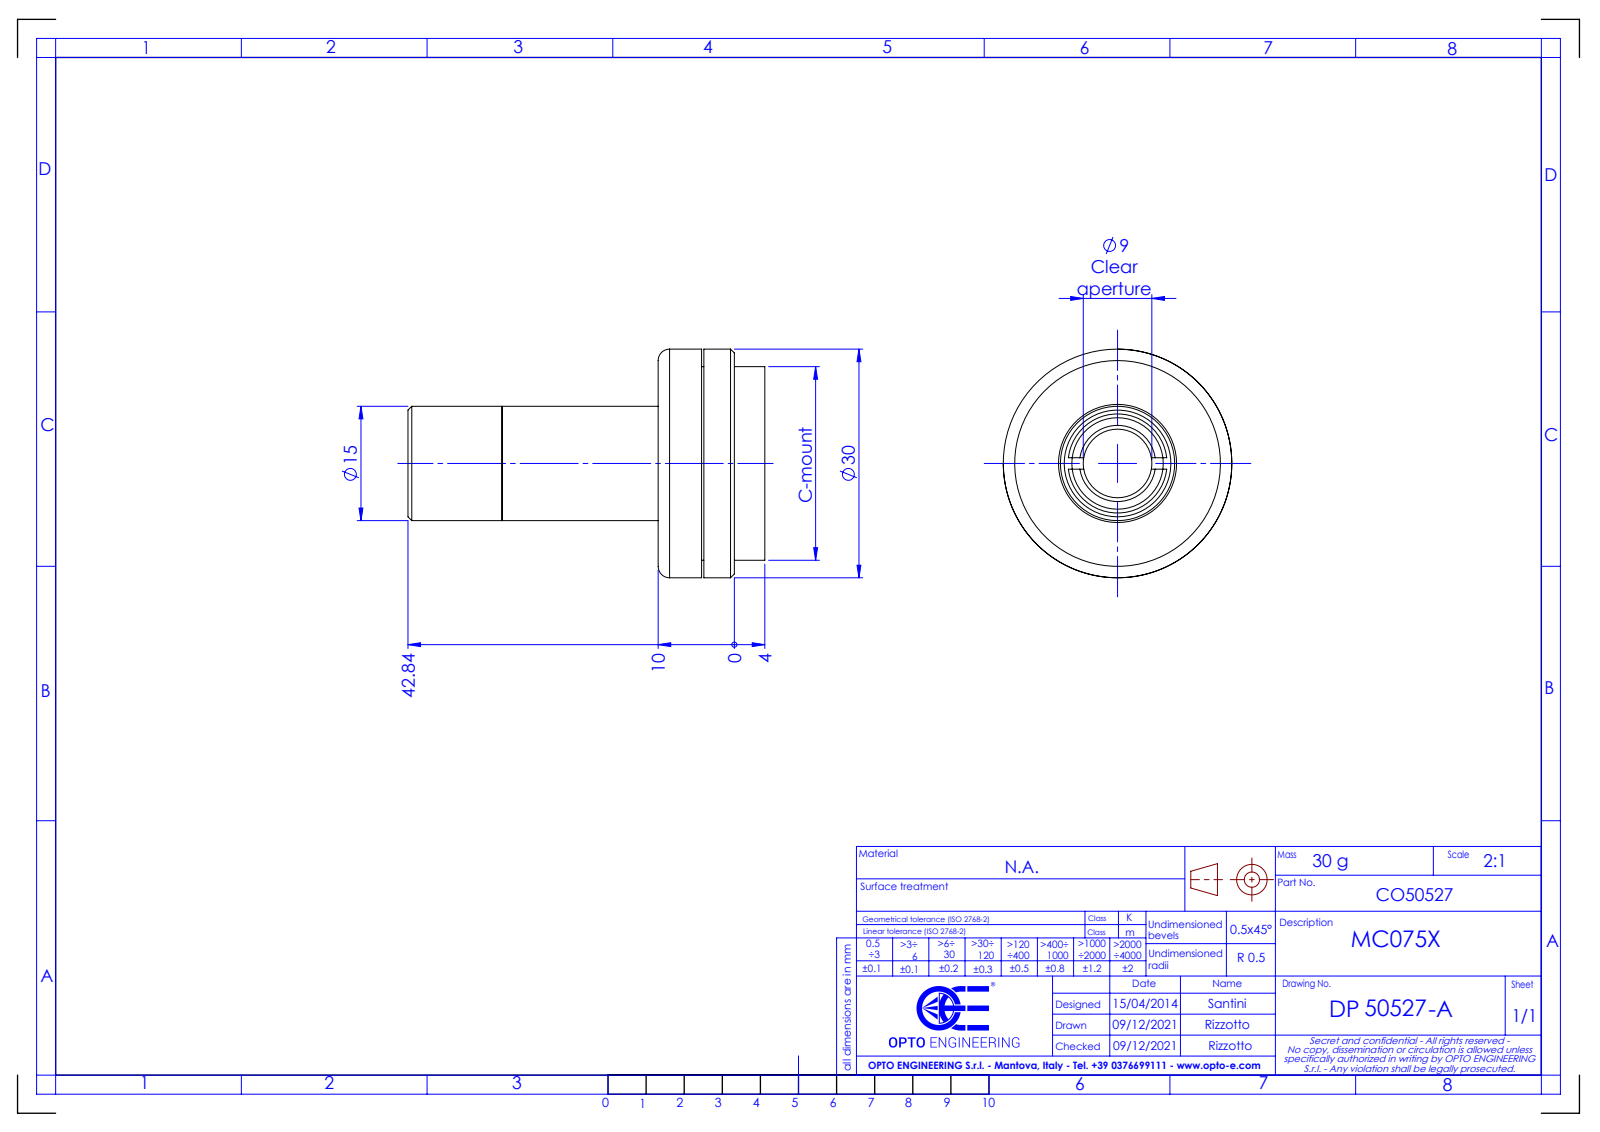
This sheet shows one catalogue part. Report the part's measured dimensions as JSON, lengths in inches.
{"part_name": "DP50527-A_MC075X", "step_written_by": "SolidWorks 2021 (CONFIG_CONTROL_DESIGN)", "units": "inches", "bodies": {"solids": 0, "faces": 49, "planar": 16, "cylindrical": 18, "other": 15}, "overall_size": [1.844, 1.181, 1.181], "round_holes": [[0.354, 1], [0.472, 1]], "round_bosses_or_shafts": [[1.181, 1], [1, 1], [0.591, 1], [0.571, 1]], "face_to_face_distances": [0.157, 0.236, 0.224, 0.394, 0.169, 0.551, 0.327, 0.315, 1.293, 1.517]}
